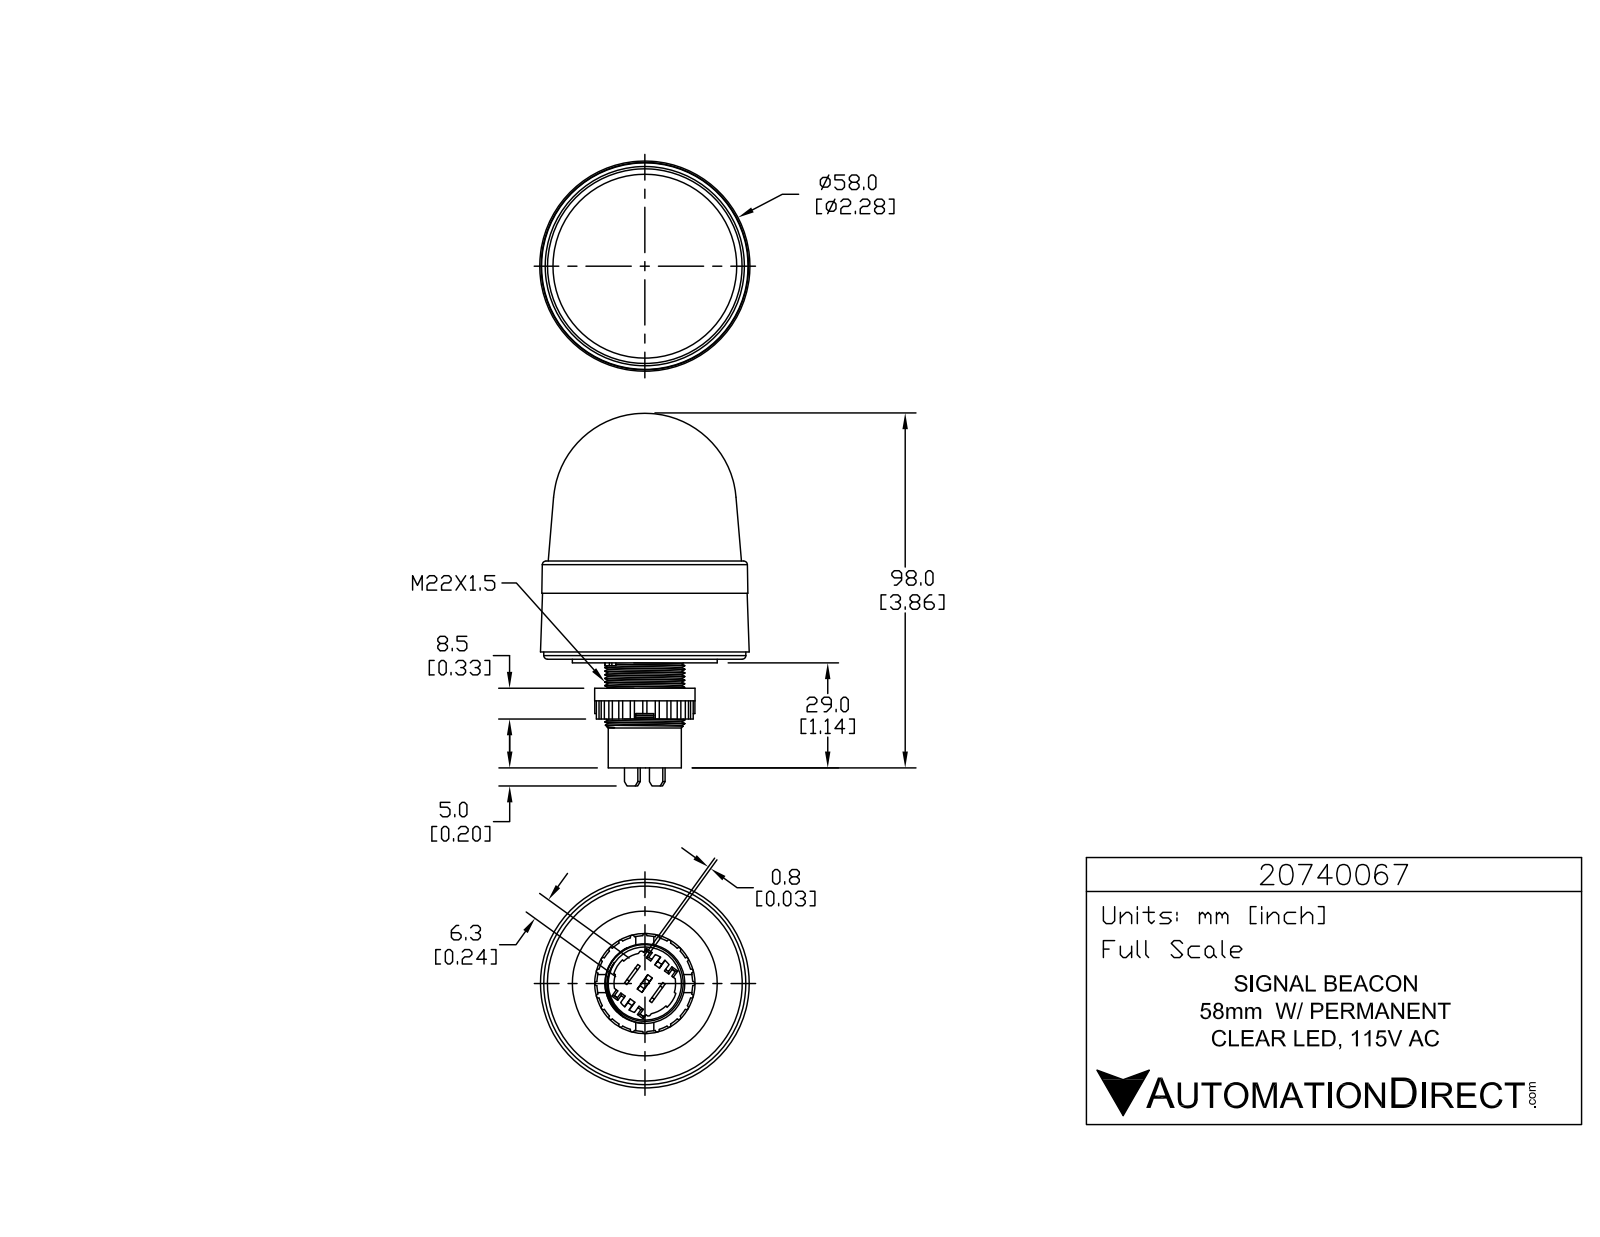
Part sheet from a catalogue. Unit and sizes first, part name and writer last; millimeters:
Units: millimetres
Overall size (bounding box): 102.9 × 57.6 × 57.6
Round holes (diameter × count): ⌀23 ×1
Round bosses / shafts (diameter × count): ⌀55.8 ×1, ⌀40 ×1, ⌀27.7 ×1, ⌀22 ×1, ⌀20.2 ×1
Partial cylindrical surfaces — rounded edges, fillets, slot ends (radius × count): R0.6 ×24, R0.5 ×2, R8.5 ×1, R9 ×1, R13.3 ×1
Main face-to-face distances: 1, 7, 3, 29, 8.5, 8, 27, 19, 26, 18.5
Volume: 147 700 mm³ · Surface area: 20 030 mm²
Bodies: 1 solid, 266 faces (119 planar, 120 cylindrical, 27 other)
Part name (STEP PRODUCT): 20740067
STEP written by: SolidWorks 2015 (AUTOMOTIVE_DESIGN)
